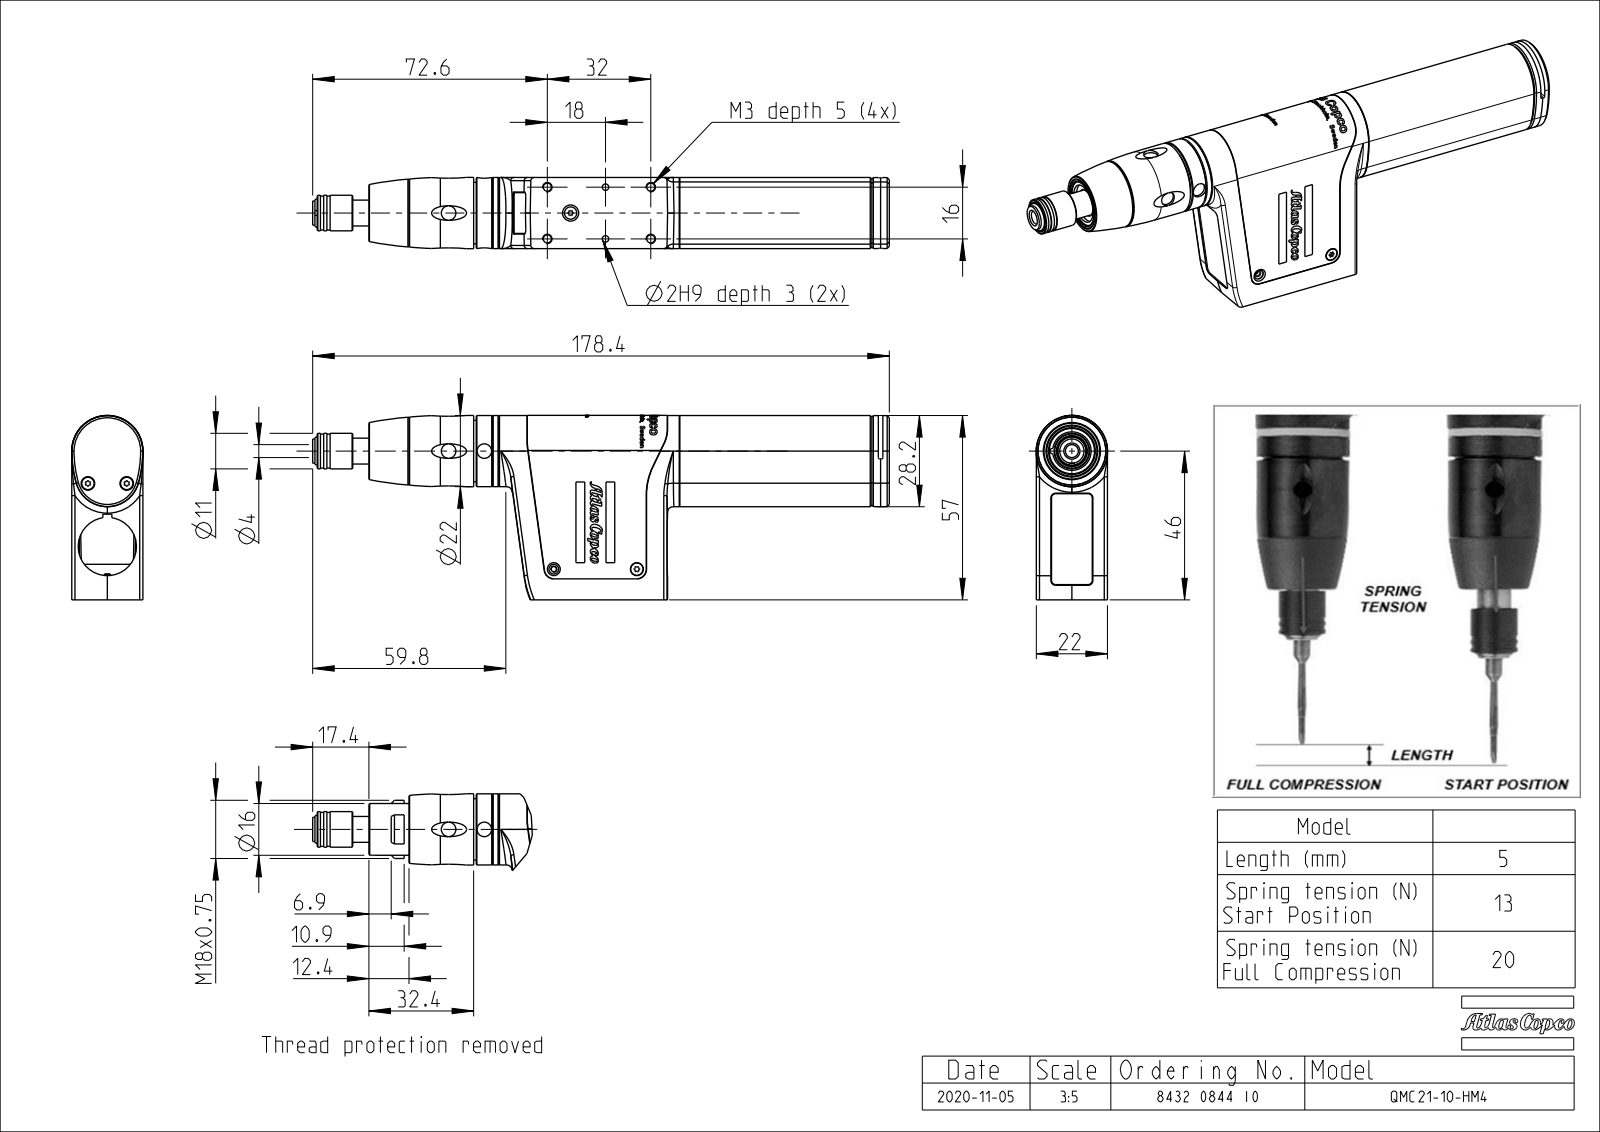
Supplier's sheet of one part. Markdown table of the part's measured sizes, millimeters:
| quantity | value |
| --- | --- |
| part name | 4216245103; 0993000295_SPEC_3; 4216240420_AF0_ASM; 4216240480_ASM (+8 more) |
| STEP written by | CREO PARAMETRIC BY PTC INC, 2016260 (CONFIG_CONTROL_DESIGN) |
| units | millimeters |
| bodies | 19 solids, 1329 faces (367 planar, 613 cylindrical, 349 other) |
| overall size | 178.4 × 57.03 × 22.06 |
| volume | 35 734 mm³ |
| surface area | 46 143 mm² |
| round holes (diameter × count) | 2.5 × 6, 2 × 5, 1.6 × 4, 1.7 × 3, 2.1 × 3, 2.2 × 3, 4.5 × 3, 1 × 2, 1.2 × 2, 2.05 × 2, 2.7 × 2, 3 × 2 |
| round bosses / shafts (diameter × count) | 1 × 12, 0.7 × 12, 0.6 × 12, 3.8 × 4, 18 × 2, 15 × 2, 2 × 2, 22 × 1 |
| partial cylindrical surfaces (radius × count) | 0.5 × 19, 3 × 16, 1 × 13, 0.1 × 12, 0.17 × 12, 0.32 × 12, 2 × 8, 0.52 × 6 |
| main face-to-face distances | 21.3, 0.5, 20.8, 21.8, 0.6, 21.4, 21.9, 22, 2, 1 |
| hole center spacings | 16, 0.5, 9.85, 10.63, 11.66, 11.93, 12.5, 13.6 |
